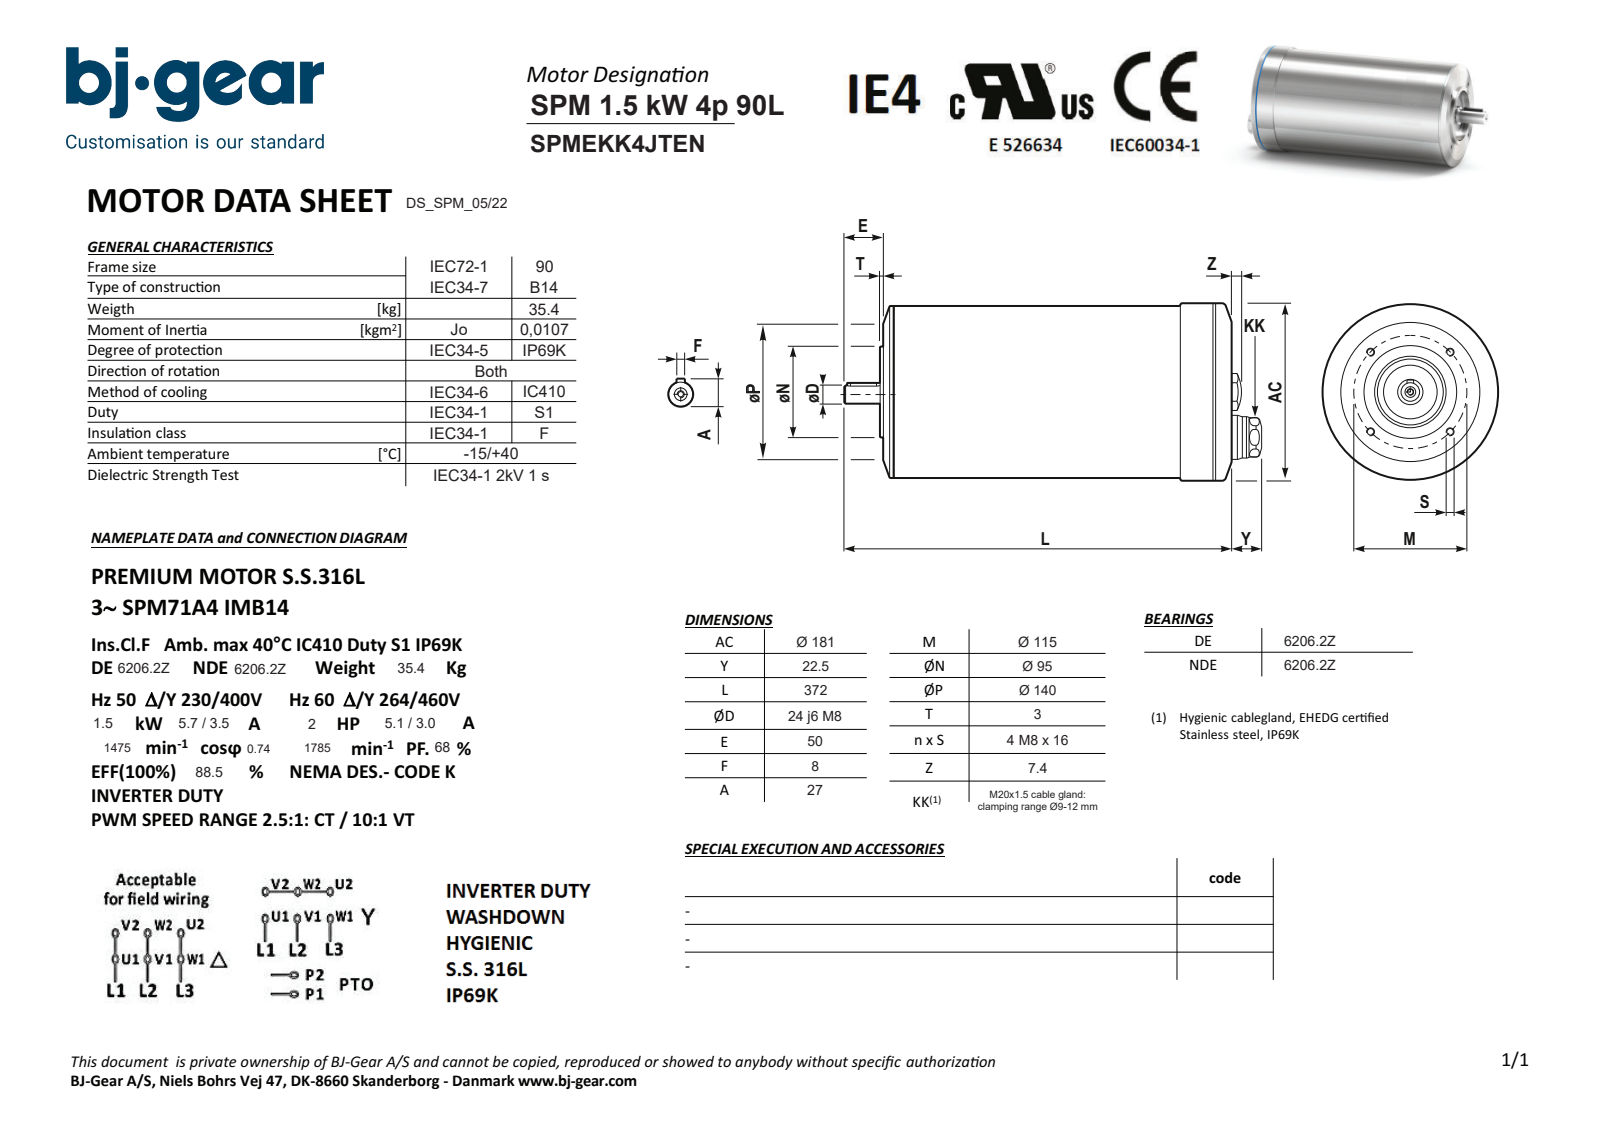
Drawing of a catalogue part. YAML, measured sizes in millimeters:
part_name: "SPMEKK4JTENN4KSA1-N---NNN"
step_written_by: "Solid Edge (AUTOMOTIVE_DESIGN)"
units: millimeters
bodies: {solids: 1, faces: 87, planar: 30, cylindrical: 32, other: 25}
overall_size: [399.5, 181, 181]
volume: 8014000
surface_area: 238617
round_holes:
  - {diameter: 6.65, count: 4}
  - {diameter: 4.92, count: 1}
  - {diameter: 7, count: 1}
  - {diameter: 8.4, count: 1}
  - {diameter: 13.4, count: 1}
  - {diameter: 85, count: 1}
round_bosses_or_shafts:
  - {diameter: 181, count: 1}
  - {diameter: 180.98, count: 1}
  - {diameter: 178, count: 1}
  - {diameter: 177.98, count: 1}
  - {diameter: 95, count: 1}
  - {diameter: 30, count: 1}
  - {diameter: 24, count: 1}
  - {diameter: 20, count: 1}
partial_cylinders:
  - {radius: 4, count: 2}
  - {radius: 12.8, count: 1}
face_to_face_distances: [322, 6, 316, 325, 9, 3, 8, 24, 50, 372]
hole_center_spacings: [57.5, 81.32, 43.11, 103.94, 115, 55]
